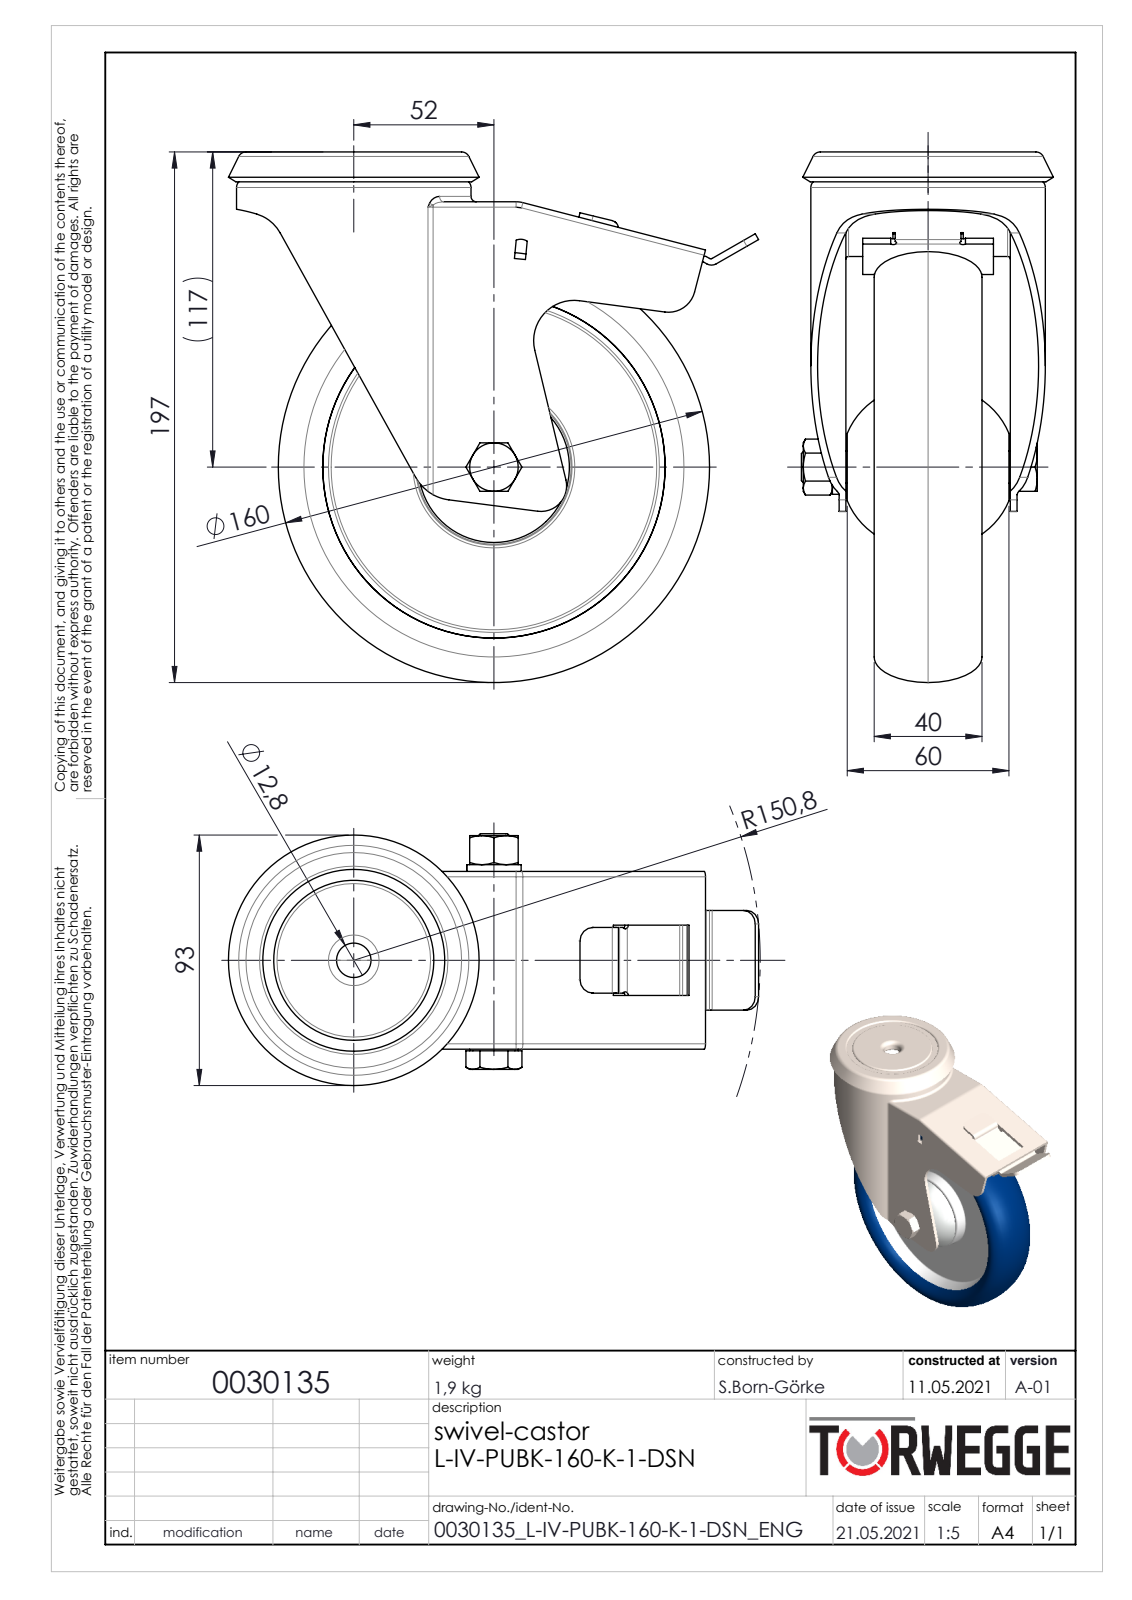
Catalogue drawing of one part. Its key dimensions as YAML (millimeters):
part_name: "0030135"
step_written_by: "SolidWorks 2020 (AUTOMOTIVE_DESIGN)"
units: millimeters
bodies: {solids: 0, faces: 506, planar: 158, cylindrical: 143, other: 205}
overall_size: [197, 196.69, 93.5]
round_holes:
  - {diameter: 10.2, count: 1}
  - {diameter: 12, count: 1}
  - {diameter: 12.2, count: 1}
  - {diameter: 12.8, count: 1}
  - {diameter: 17, count: 1}
  - {diameter: 45, count: 1}
  - {diameter: 47, count: 1}
  - {diameter: 70, count: 1}
  - {diameter: 87, count: 1}
round_bosses_or_shafts:
  - {diameter: 82, count: 1}
  - {diameter: 54, count: 1}
  - {diameter: 41, count: 1}
  - {diameter: 25.2, count: 1}
  - {diameter: 20.2, count: 1}
  - {diameter: 20, count: 1}
  - {diameter: 18.2, count: 1}
  - {diameter: 18, count: 1}
partial_cylinders:
  - {radius: 34.9, count: 22}
  - {radius: 1, count: 6}
  - {radius: 1.25, count: 6}
  - {radius: 2, count: 4}
  - {radius: 5, count: 4}
  - {radius: 3, count: 3}
  - {radius: 3.5, count: 3}
  - {radius: 10, count: 2}
face_to_face_distances: [2.5, 28.25, 37.75, 63.5, 25.75, 35.25, 9.5, 66, 61, 3]
